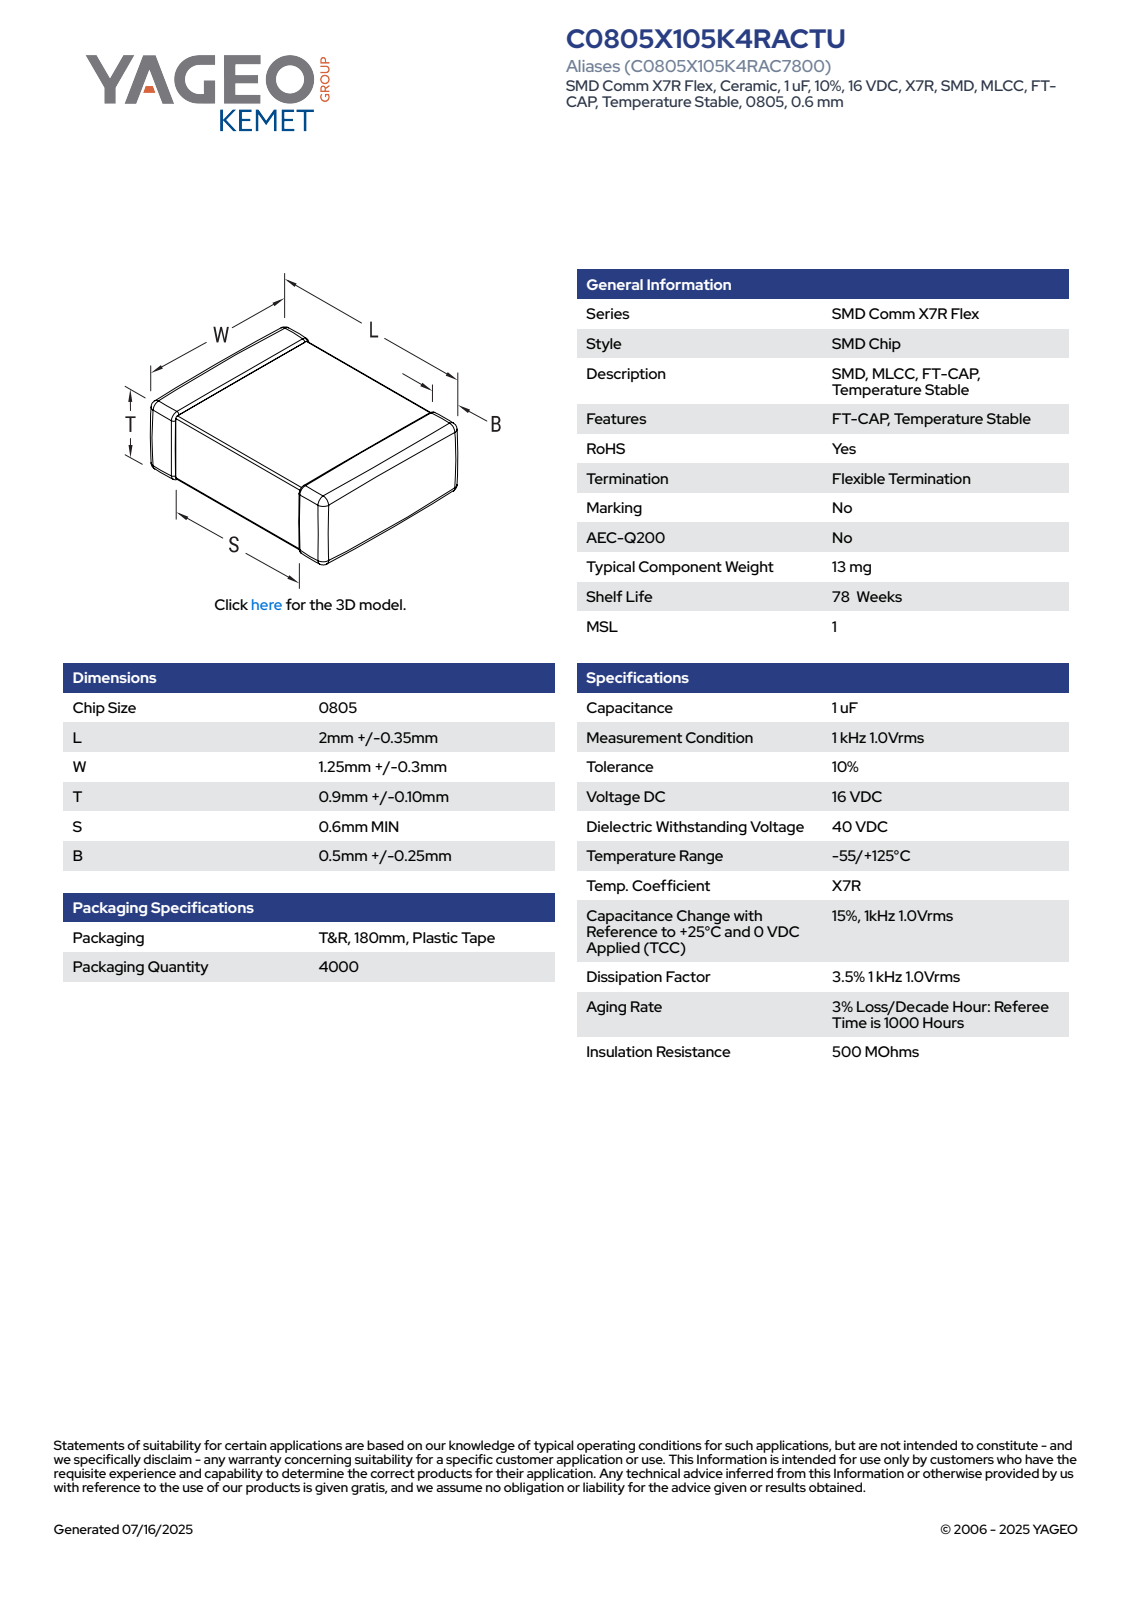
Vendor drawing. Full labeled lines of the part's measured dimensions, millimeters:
Part name (STEP PRODUCT): CCS_CCSTD_0805_L2.35W1.55T1B0.5
STEP written by: SolidWorks 2021 (AUTOMOTIVE_DESIGN)
Units: millimetres
Bodies: 4 solids, 125 faces (71 planar, 38 cylindrical, 16 other)
Overall size (bounding box): 2.35 × 1.55 × 1
Volume: 4 mm³ · Surface area: 15 mm²
Main face-to-face distances: 0.97, 1, 1.52, 2.35, 1.55, 0.94, 1.49, 1.04, 1.31, 1.08
